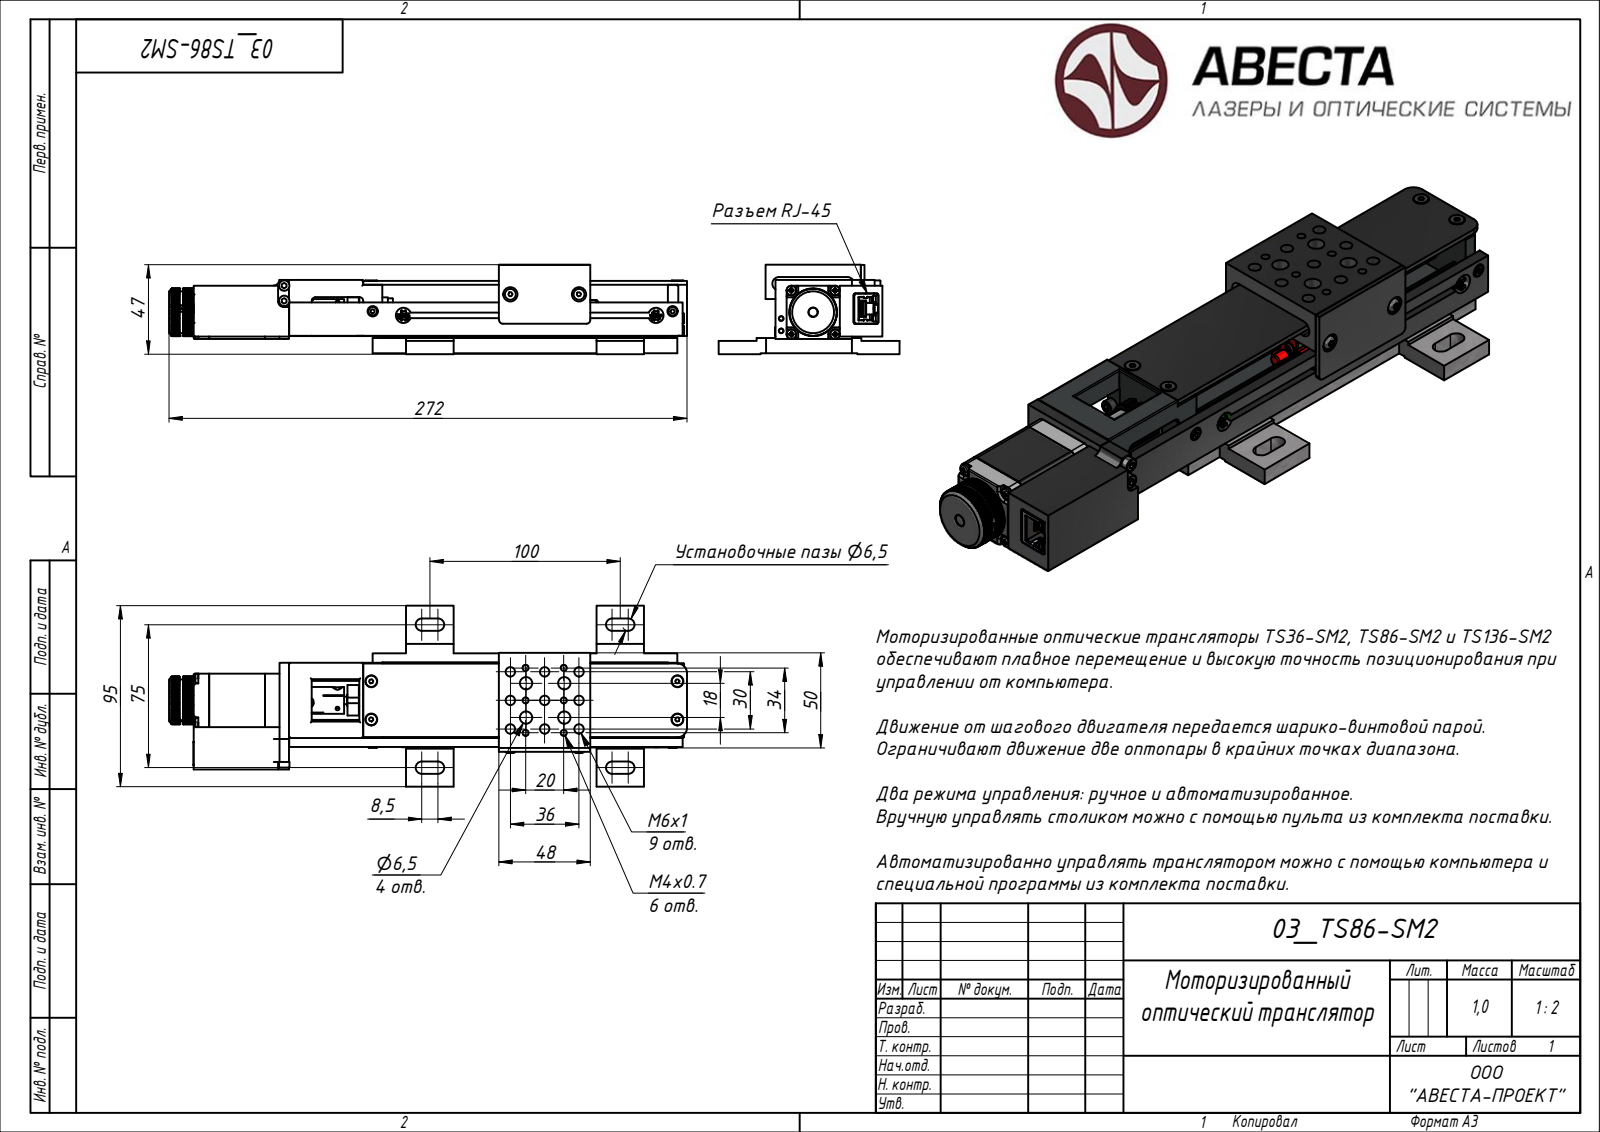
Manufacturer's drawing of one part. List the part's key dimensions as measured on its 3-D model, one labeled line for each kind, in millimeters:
STEP written by: Rhino 7.34 (AUTOMOTIVE_DESIGN)
Units: millimetres
Bodies: 1 solid, 2337 faces (1428 planar, 634 cylindrical, 275 other)
Overall size (bounding box): 272 × 95 × 47
Volume: 290 362 mm³ · Surface area: 124 577 mm²
Round holes (diameter × count): ⌀3.4 ×14, ⌀6.5 ×10, ⌀2.5 ×7, ⌀2.46 ×6, ⌀3.24 ×6, ⌀4.92 ×6, ⌀1.05 ×5, ⌀5 ×4, ⌀2.15 ×3, ⌀7.5 ×3, ⌀2.46 ×2, ⌀2.9 ×2
Round bosses / shafts (diameter × count): ⌀4.5 ×10, ⌀5.5 ×6, ⌀6 ×5, ⌀5.3 ×4, ⌀3 ×4, ⌀2.5 ×4, ⌀5 ×3, ⌀5.7 ×2
Partial cylindrical surfaces — rounded edges, fillets, slot ends (radius × count): R0.5 ×36, R2.5 ×10, R3 ×10, R2 ×8, R3.25 ×8, R1 ×4, R1.01 ×2, R1.01 ×2
Main face-to-face distances: 0.5, 2, 8, 7, 5.5, 38, 8.5, 5, 28, 2.5
Hole centre spacings: 18, 20, 9, 17, 10, 20.02, 26, 8.01
